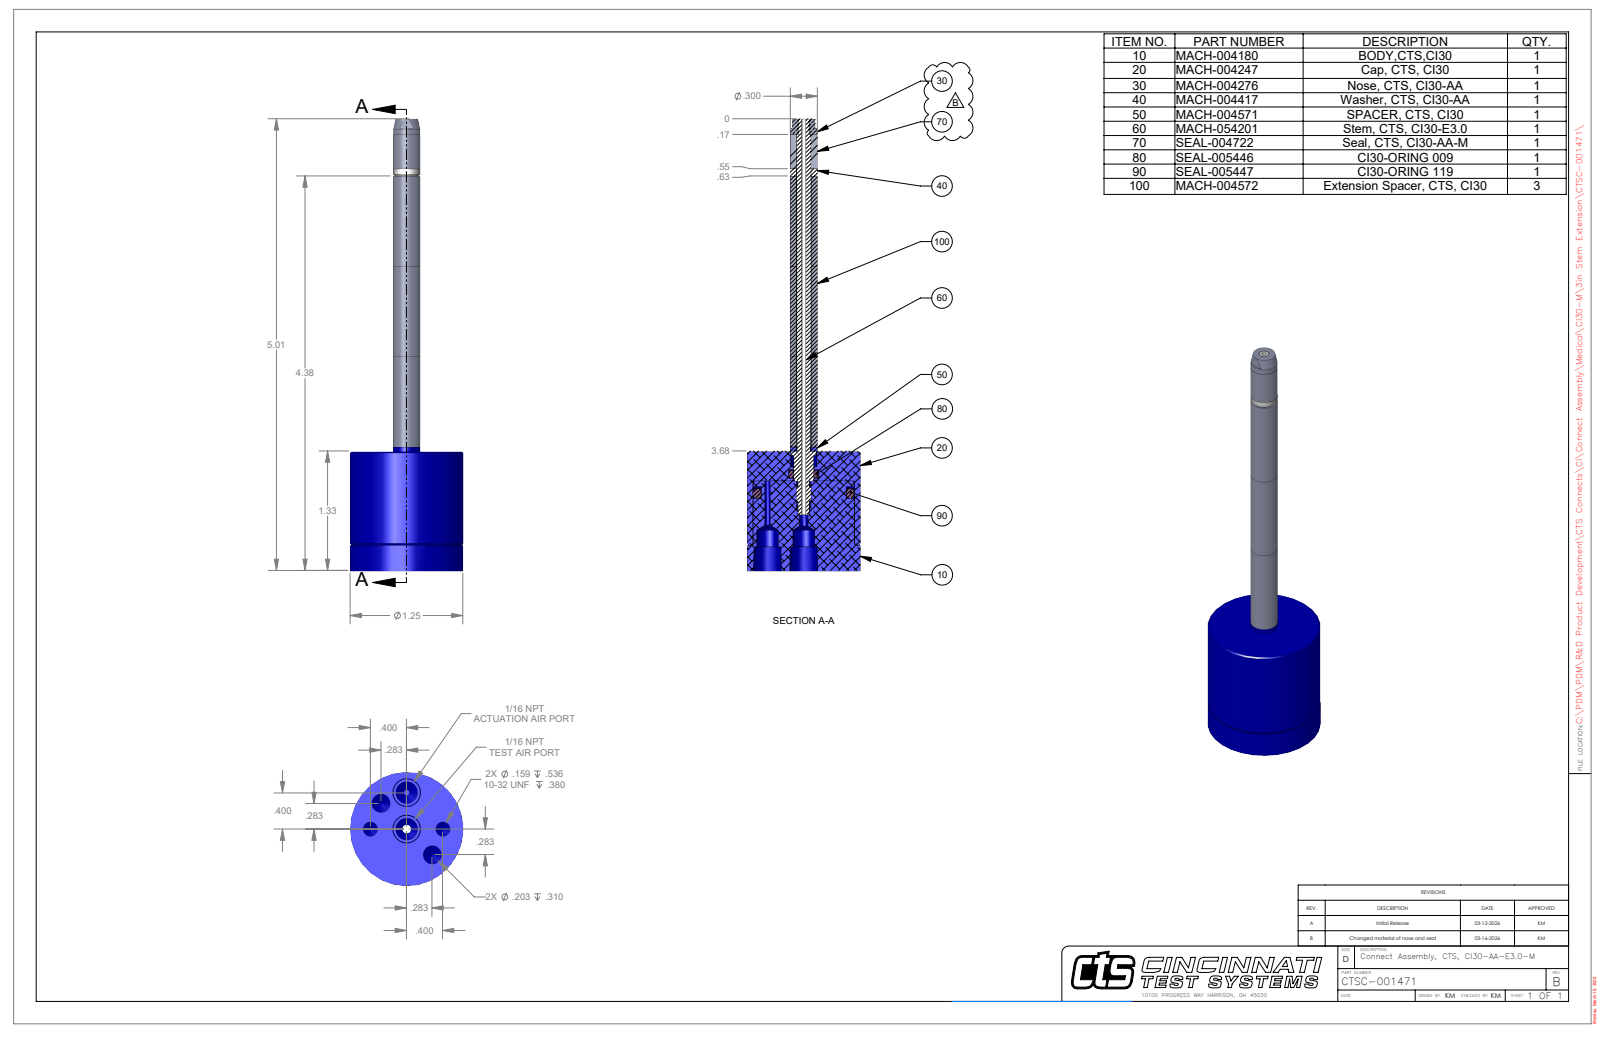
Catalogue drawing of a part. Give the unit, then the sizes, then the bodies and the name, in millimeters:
Units: millimetres
Overall size (bounding box): 127.23 × 31.75 × 31.75
Round holes (diameter × count): ⌀4.04 ×2, ⌀5.16 ×2, ⌀6.15 ×2, ⌀1.32 ×1, ⌀2.38 ×1, ⌀2.87 ×1, ⌀3.94 ×1, ⌀4.18 ×1, ⌀7.34 ×1, ⌀28.58 ×1
Round bosses / shafts (diameter × count): ⌀31.75 ×1, ⌀28.32 ×1, ⌀7.62 ×1, ⌀7.56 ×1, ⌀7.04 ×1, ⌀3.94 ×1, ⌀3.51 ×1
Main face-to-face distances: 33.66, 25.4, 50.8, 7.28, 26.38, 7.37, 26.29, 122.81, 115.53, 115.44
Hole centre spacings: 7.77, 10.16, 18.77, 10.15, 14.37, 20.31, 20.32
Volume: 28 870 mm³ · Surface area: 12 776 mm²
Bodies: 8 solids, 84 faces (37 planar, 30 cylindrical, 17 other)
Part name (STEP PRODUCT): CTSC-001471
STEP written by: SolidWorks 2023 (AUTOMOTIVE_DESIGN)
